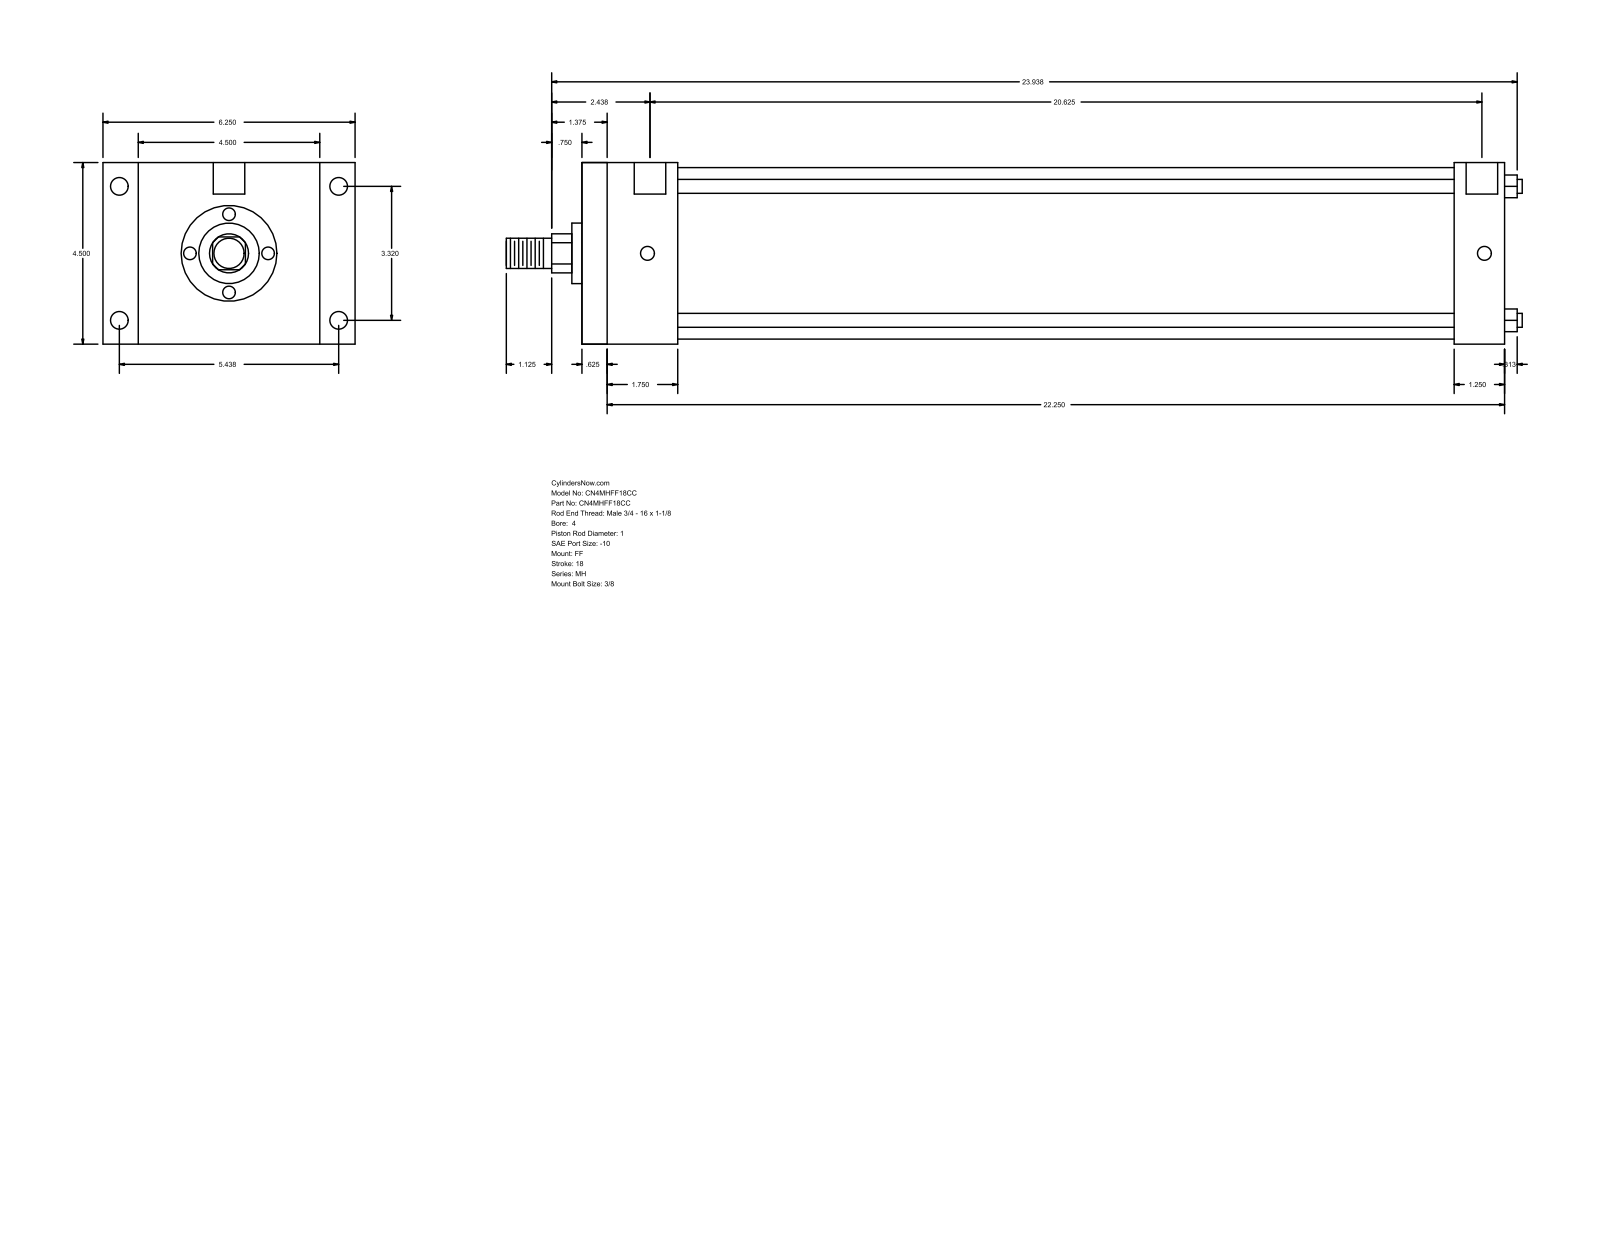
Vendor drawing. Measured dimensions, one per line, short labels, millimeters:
name: MH_FF__0400_1
written by: GSSL Pune (CONFIG_CONTROL_DESIGN)
unit: mm
bodies: 0 solids, 92 faces (64 planar, 28 cylindrical, 0 other)
size: 639.76 × 158.75 × 114.3
holes: 4× ⌀8.73, 4× ⌀11.13, 2× ⌀19.84
bosses: 4× ⌀8.76, 1× ⌀107.95, 1× ⌀38.1, 1× ⌀25.4, 1× ⌀19.05
rounds: 1× R12.29
face distances: 114.3, 581.03, 15.87, 565.16, 60.33, 44.46, 520.7, 549.28, 533.41, 488.95
hole spacings: 84.32, 138.12, 161.82, 527.05, 1.58, 1.59, 523.88, 525.46
